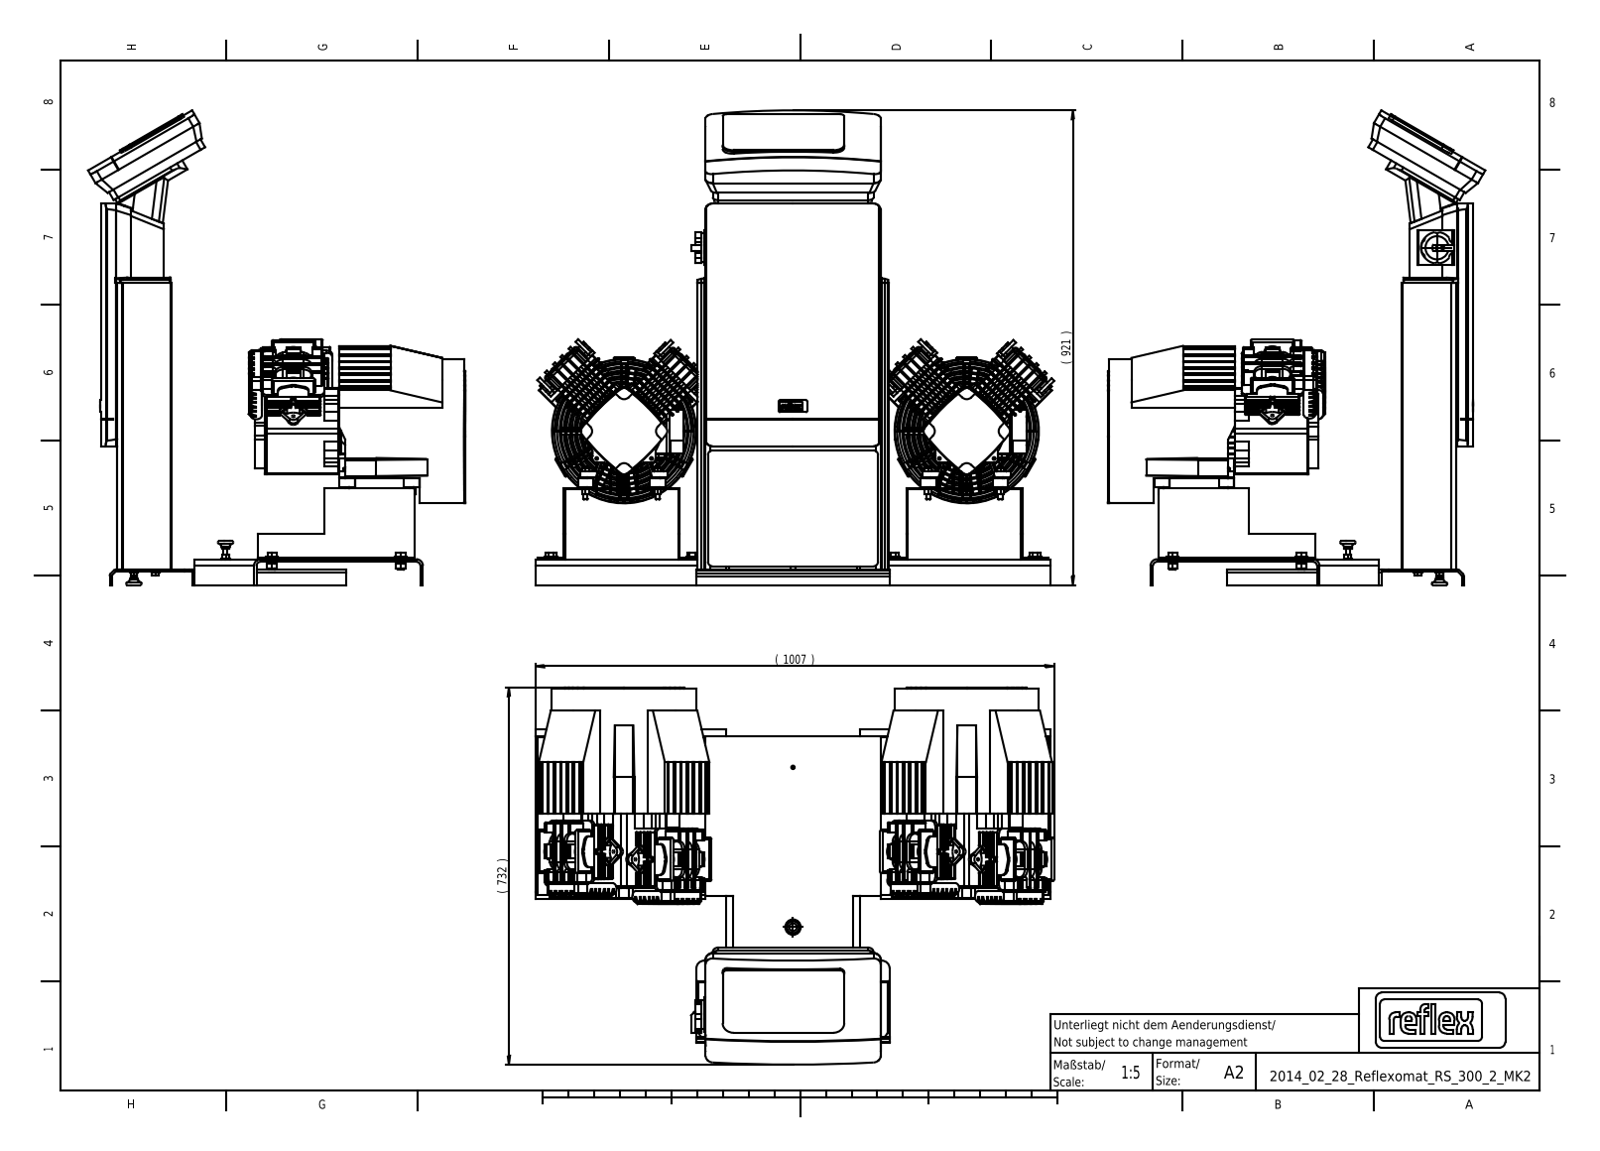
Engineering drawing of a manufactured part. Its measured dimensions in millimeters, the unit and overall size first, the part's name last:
Units: millimetres
Overall size (bounding box): 1006.88 × 920.68 × 731.66
Round holes (diameter × count): ⌀5.5 ×22, ⌀7 ×22, ⌀17.5 ×13, ⌀10.5 ×10, ⌀6 ×8, ⌀6.5 ×8, ⌀13 ×8, ⌀17 ×8, ⌀9 ×4, ⌀13.5 ×4, ⌀15 ×4, ⌀5.4 ×3
Round bosses / shafts (diameter × count): ⌀20 ×14, ⌀16 ×13, ⌀8 ×13, ⌀19 ×10, ⌀11.2 ×9, ⌀5.1 ×9, ⌀30 ×8, ⌀24 ×8
Partial cylindrical surfaces — rounded edges, fillets, slot ends (radius × count): R1.6 ×280, R5 ×73, R1 ×71, R10 ×48, R2 ×43, R2.5 ×36, R15 ×34, R8 ×28
Main face-to-face distances: 5, 15, 3, 159, 4, 24, 20, 1, 19, 135
Hole centre spacings: 31, 665, 62, 89.08, 45, 108, 77.75, 25.36
Volume: 46 870 000 mm³ · Surface area: 6 767 000 mm²
Bodies: 111 solids, 9333 faces (4541 planar, 3186 cylindrical, 1606 other)
STEP written by: Mechanical Desktop 2011 (CONFIG_CONTROL_DESIGN)
